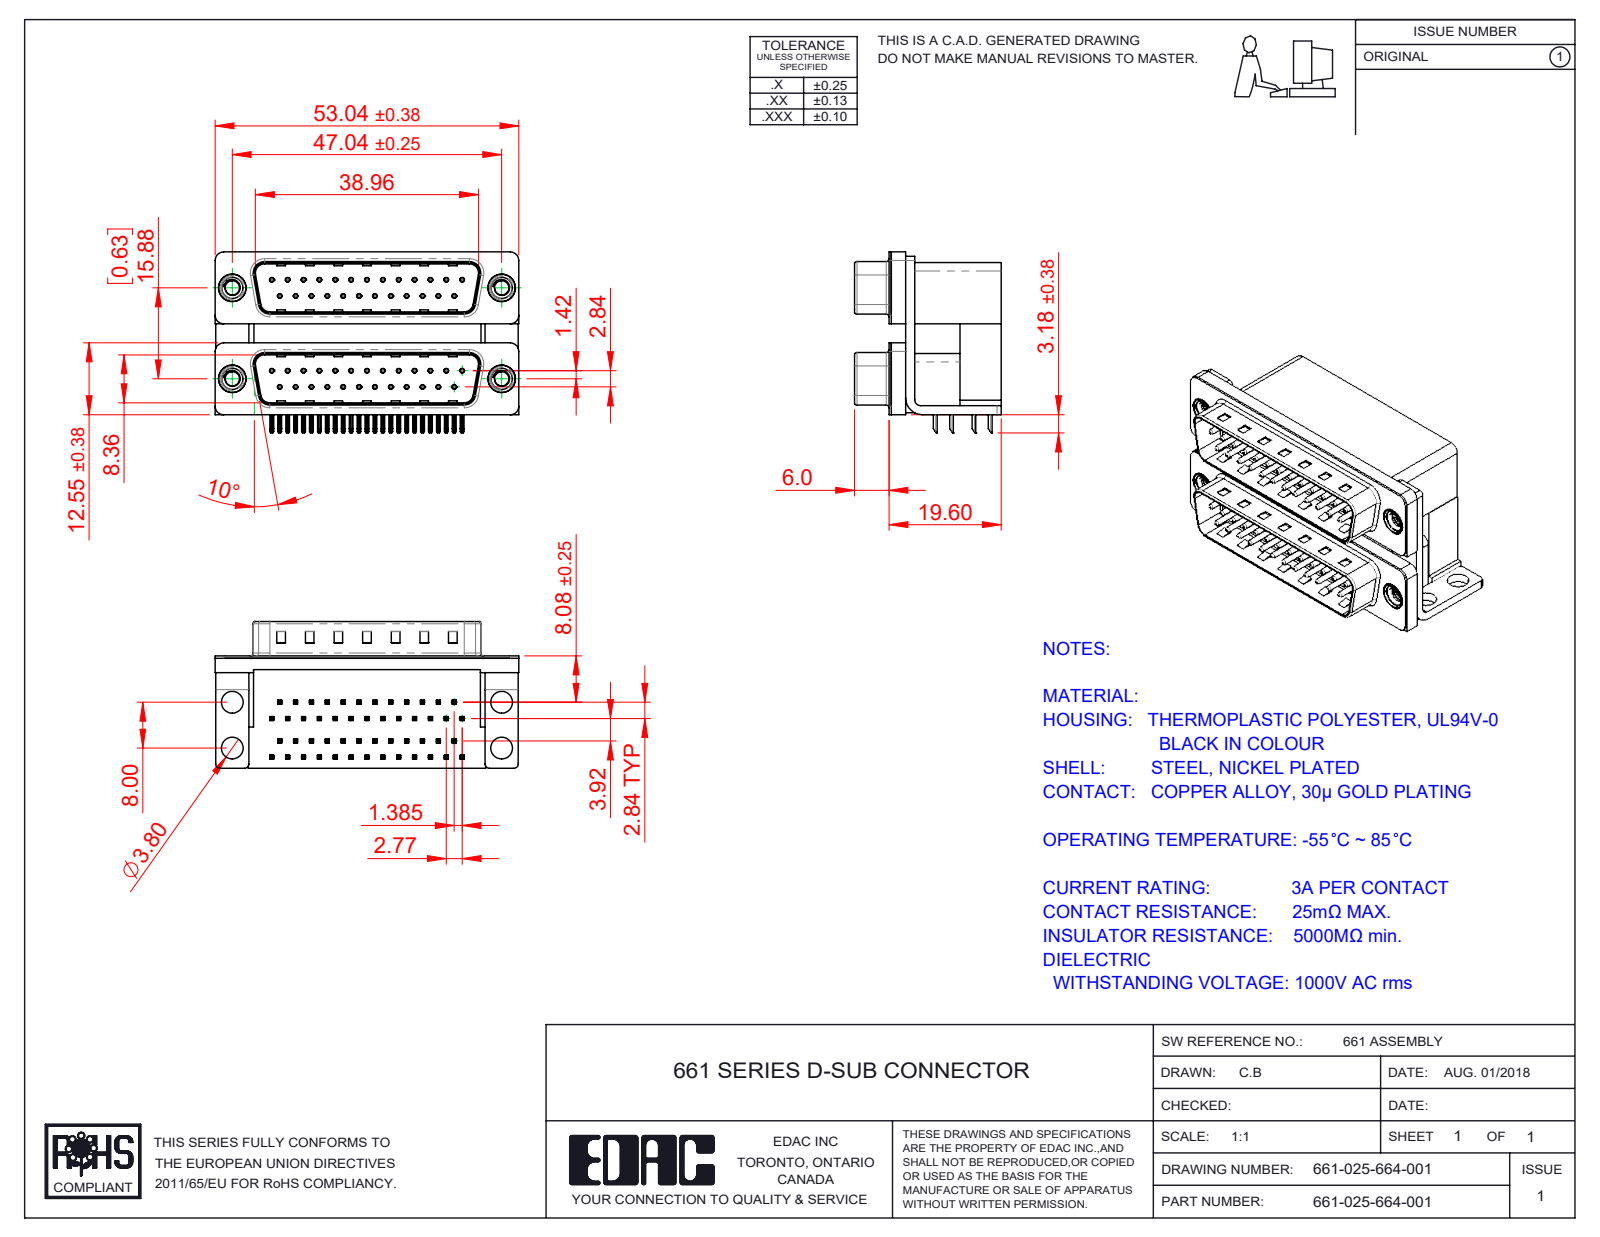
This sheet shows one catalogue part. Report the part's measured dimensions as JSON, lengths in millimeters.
{"part_name": "661 Contact Bottom Upper_L; 661 Housing Spacer_25 Contacts L; 661 Mounting Bracket_NoneL; 661 Contact Bottom Lower (+7 more)", "step_written_by": "SolidWorks 2020 (CONFIG_CONTROL_DESIGN)", "units": "millimeters", "bodies": {"solids": 61, "faces": 4598, "planar": 2934, "cylindrical": 1274, "other": 390}, "overall_size": [53.04, 31.61, 25.6], "volume_mm3": 20053, "surface_area_mm2": 20798, "round_holes": [[0.35, 50], [0.8, 50], [2.5, 4], [3.5, 4], [4, 4], [4.8, 4], [5, 4]], "round_bosses_or_shafts": [[0.75, 50], [4.9, 4], [4.75, 4], [3.9, 4]], "partial_cylinders_radius": [[0.25, 200], [0.12, 100], [0.5, 16], [1.5, 13], [0.9, 8], [1.6, 8], [2, 8], [0.4, 4]], "face_to_face_distances": [0.4, 19.2, 7.2, 12, 15.87, 10.7, 16.7, 9.5, 2.5, 15.53], "hole_center_spacings": [3.16, 2.77, 5.54, 8.31, 11.08, 13.85, 16.62, 5.03]}
